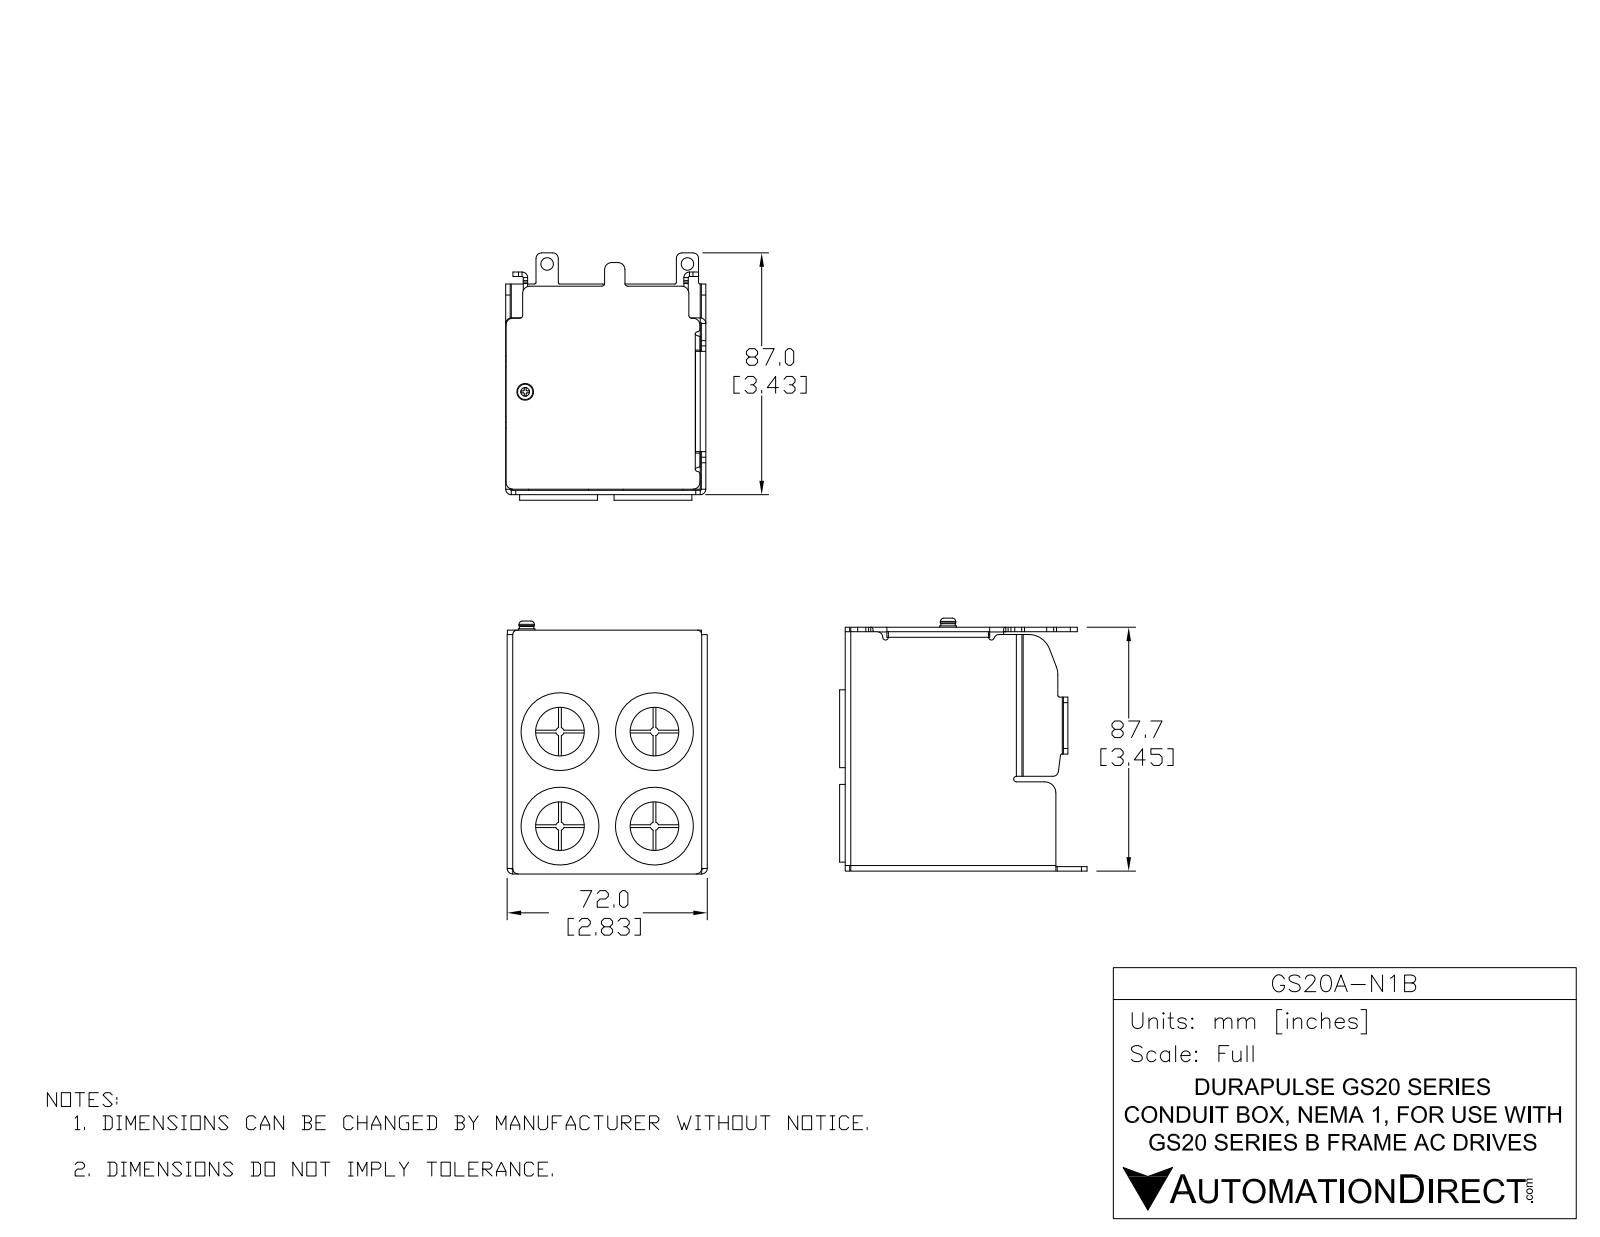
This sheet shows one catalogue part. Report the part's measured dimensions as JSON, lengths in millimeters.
{"part_name": "GS20A-N1A3", "step_written_by": "SolidWorks 2017 (AUTOMOTIVE_DESIGN)", "units": "millimeters", "bodies": {"solids": 12, "faces": 486, "planar": 232, "cylindrical": 200, "other": 54}, "overall_size": [93.5, 89, 72], "volume_mm3": 54470, "surface_area_mm2": 71480, "round_holes": [[17.5, 4], [22.5, 4], [3, 3], [3.3, 2], [4.5, 2], [2.5, 1], [4, 1]], "round_bosses_or_shafts": [[28, 4], [21.5, 4], [8, 2], [7.9, 2], [6.9, 2], [6.6, 2], [5.4, 2], [4, 2]], "partial_cylinders_radius": [[2, 31], [1, 15], [0.4, 12], [2.5, 10], [0.5, 6], [0.3, 4], [1.5, 4], [0.8, 2]], "face_to_face_distances": [1.6, 70.4, 86.1, 84.5, 72, 68.8, 87.7, 6.3, 64.1, 2], "hole_center_spacings": [34, 48.1, 20.7, 22.4, 29.5, 44.7, 46.5, 48.6]}
